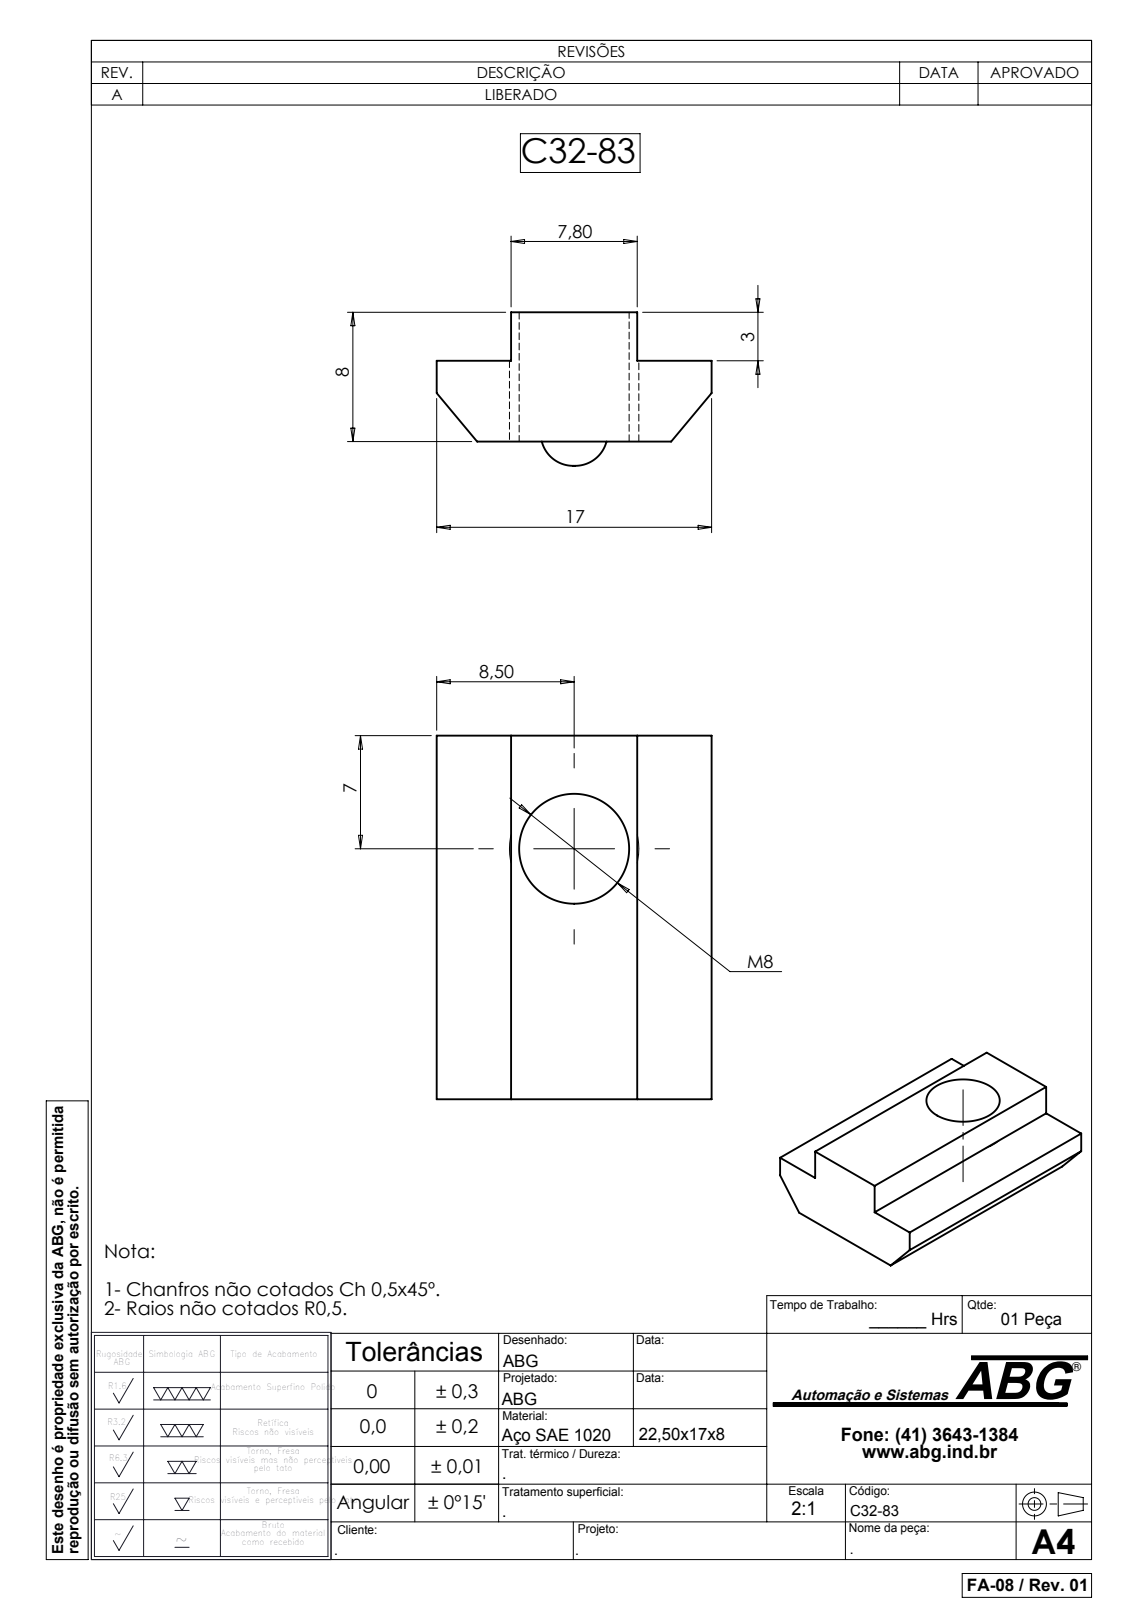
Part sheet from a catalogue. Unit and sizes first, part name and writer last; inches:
Units: inches
Overall size (bounding box): 0.886 × 0.669 × 0.374
Round holes (diameter × count): ⌀0.268 ×1
Main face-to-face distances: 0.197, 0.315, 0.118, 0.886, 0.181, 0.488, 0.307, 0.669, 0.059, 0.256
Volume: 0.121 in³ · Surface area: 2.11 in²
Bodies: 1 solid, 17 faces (13 planar, 2 cylindrical, 2 other)
Part name (STEP PRODUCT): C32-83
STEP written by: SolidWorks 2007 (CONFIG_CONTROL_DESIGN)
